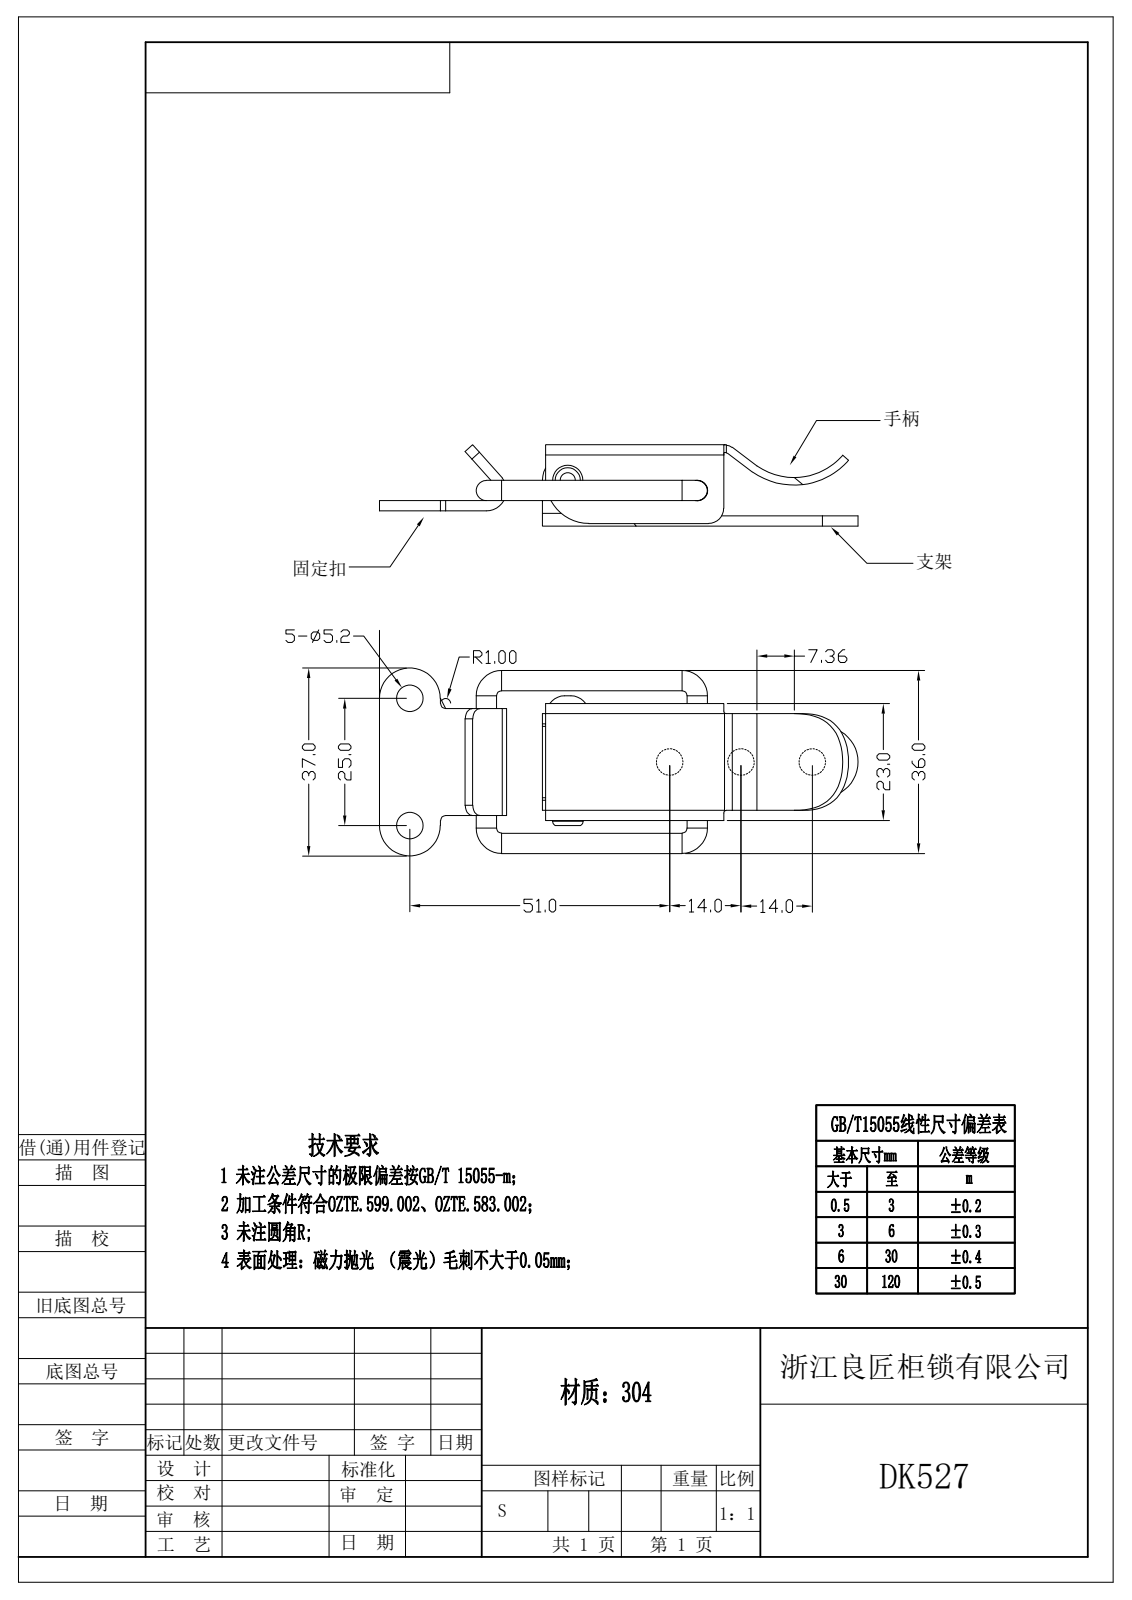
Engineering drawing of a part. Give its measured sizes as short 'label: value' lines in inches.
written by: Rhino 8.5 (CONFIG_CONTROL_DESIGN)
unit: in
bodies: 4 solids, 131 faces (53 planar, 59 cylindrical, 19 other)
size: 3.821 × 1.535 × 0.67
volume: 0.454 in³; area: 18.16 in²
holes: 3× ⌀0.205, 1× ⌀0.169, 1× ⌀0.177
bosses: 4× ⌀0.157, 2× ⌀0.205, 1× ⌀0.264
rounds: 4× R0.02, 2× R0.012, 2× R0.051, 2× R0.079, 2× R0.098, 1× R0.118, 1× R0.157, 1× R0.197
face distances: 0.079, 0.059, 0.152, 0.846, 0.571, 0.551, 0.63, 0.492, 0.074, 0.419
hole spacings: 0.551, 1.004, 1.102
